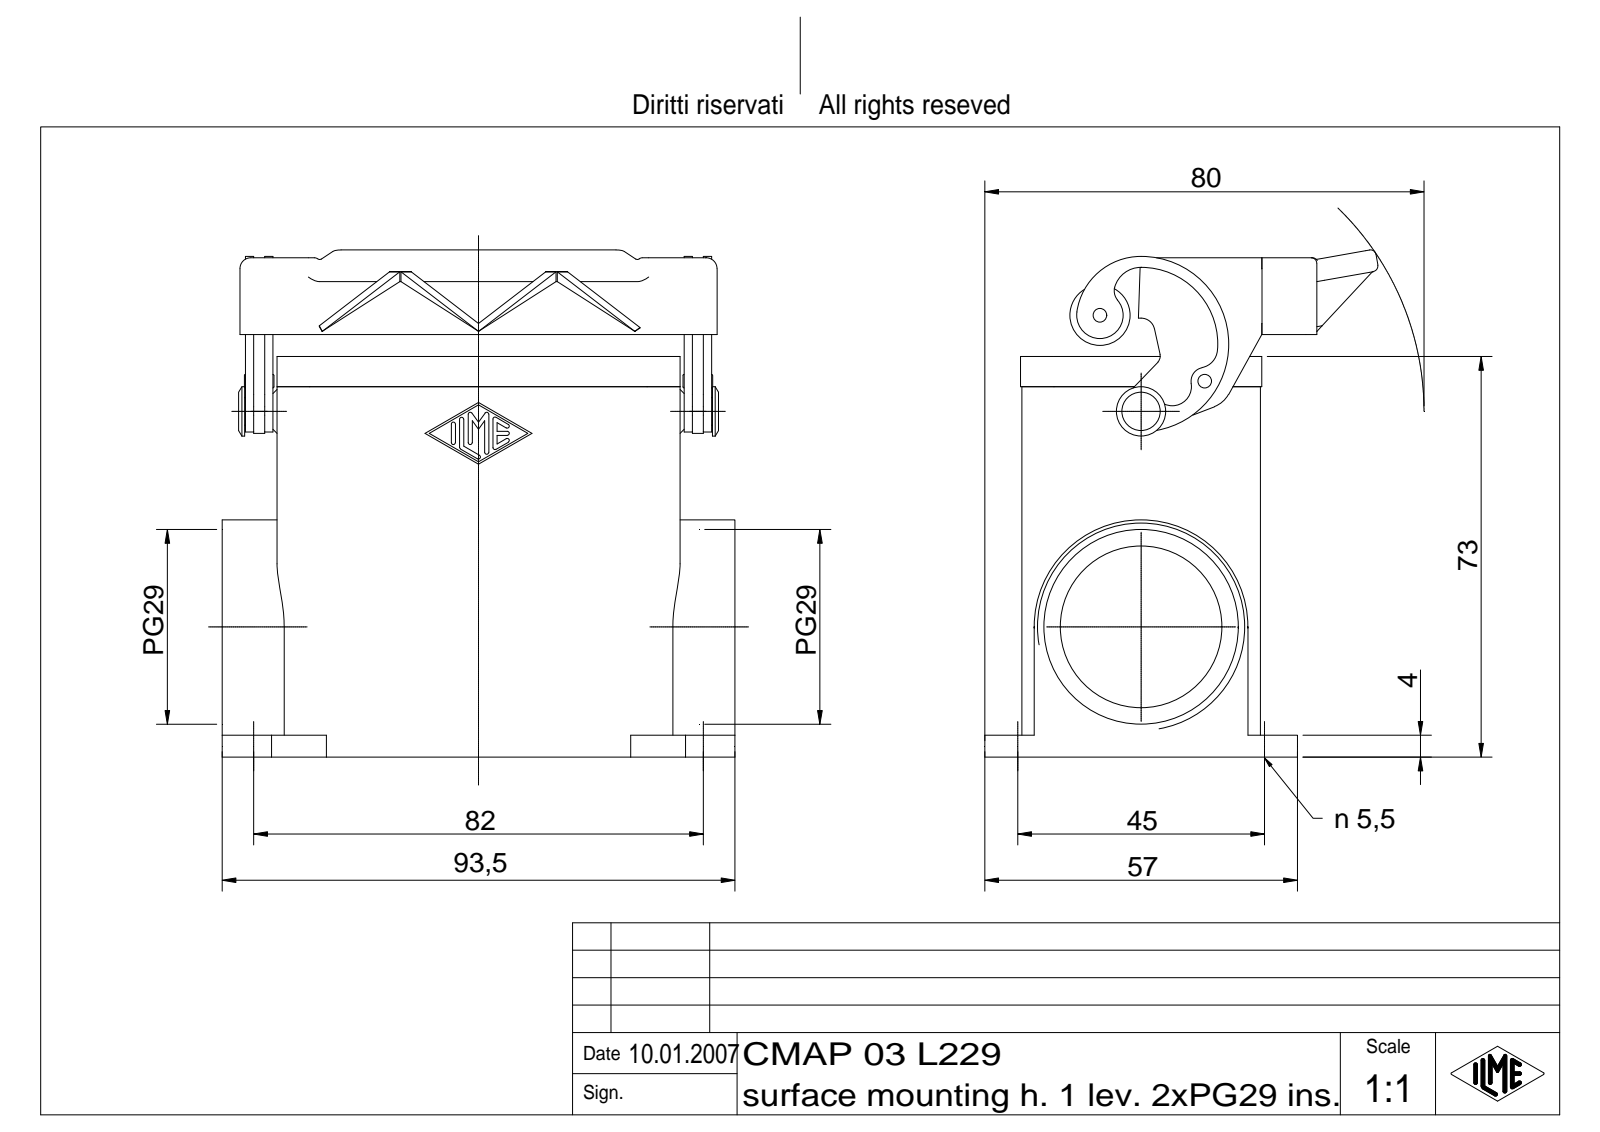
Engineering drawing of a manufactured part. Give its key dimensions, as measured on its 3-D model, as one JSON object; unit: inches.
{"part_name": "CMAP 03 L229", "step_written_by": "Autodesk Inventor 7 (AUTOMOTIVE_DESIGN)", "units": "inches", "bodies": {"solids": 4, "faces": 434, "planar": 164, "cylindrical": 125, "other": 145}, "overall_size": [3.681, 3.639, 2.823], "volume_in3": 5.958, "surface_area_in2": 83.31, "round_holes": [[0.217, 4], [0.079, 1], [1.161, 1], [1.397, 1]], "round_bosses_or_shafts": [[0.433, 1], [0.354, 1], [0.197, 1], [0.118, 1], [0.098, 1]], "partial_cylinders_radius": [[0.015, 14], [0.079, 12], [0.236, 8], [0.039, 7], [0.059, 5], [0.118, 4], [0.098, 3], [0.138, 2]], "face_to_face_distances": [0.118, 1.594, 0.157, 1.713, 1.476, 2.657, 0.344, 0.463, 2.431, 2.776], "hole_center_spacings": [1.772, 3.228, 3.683, 1.82]}
